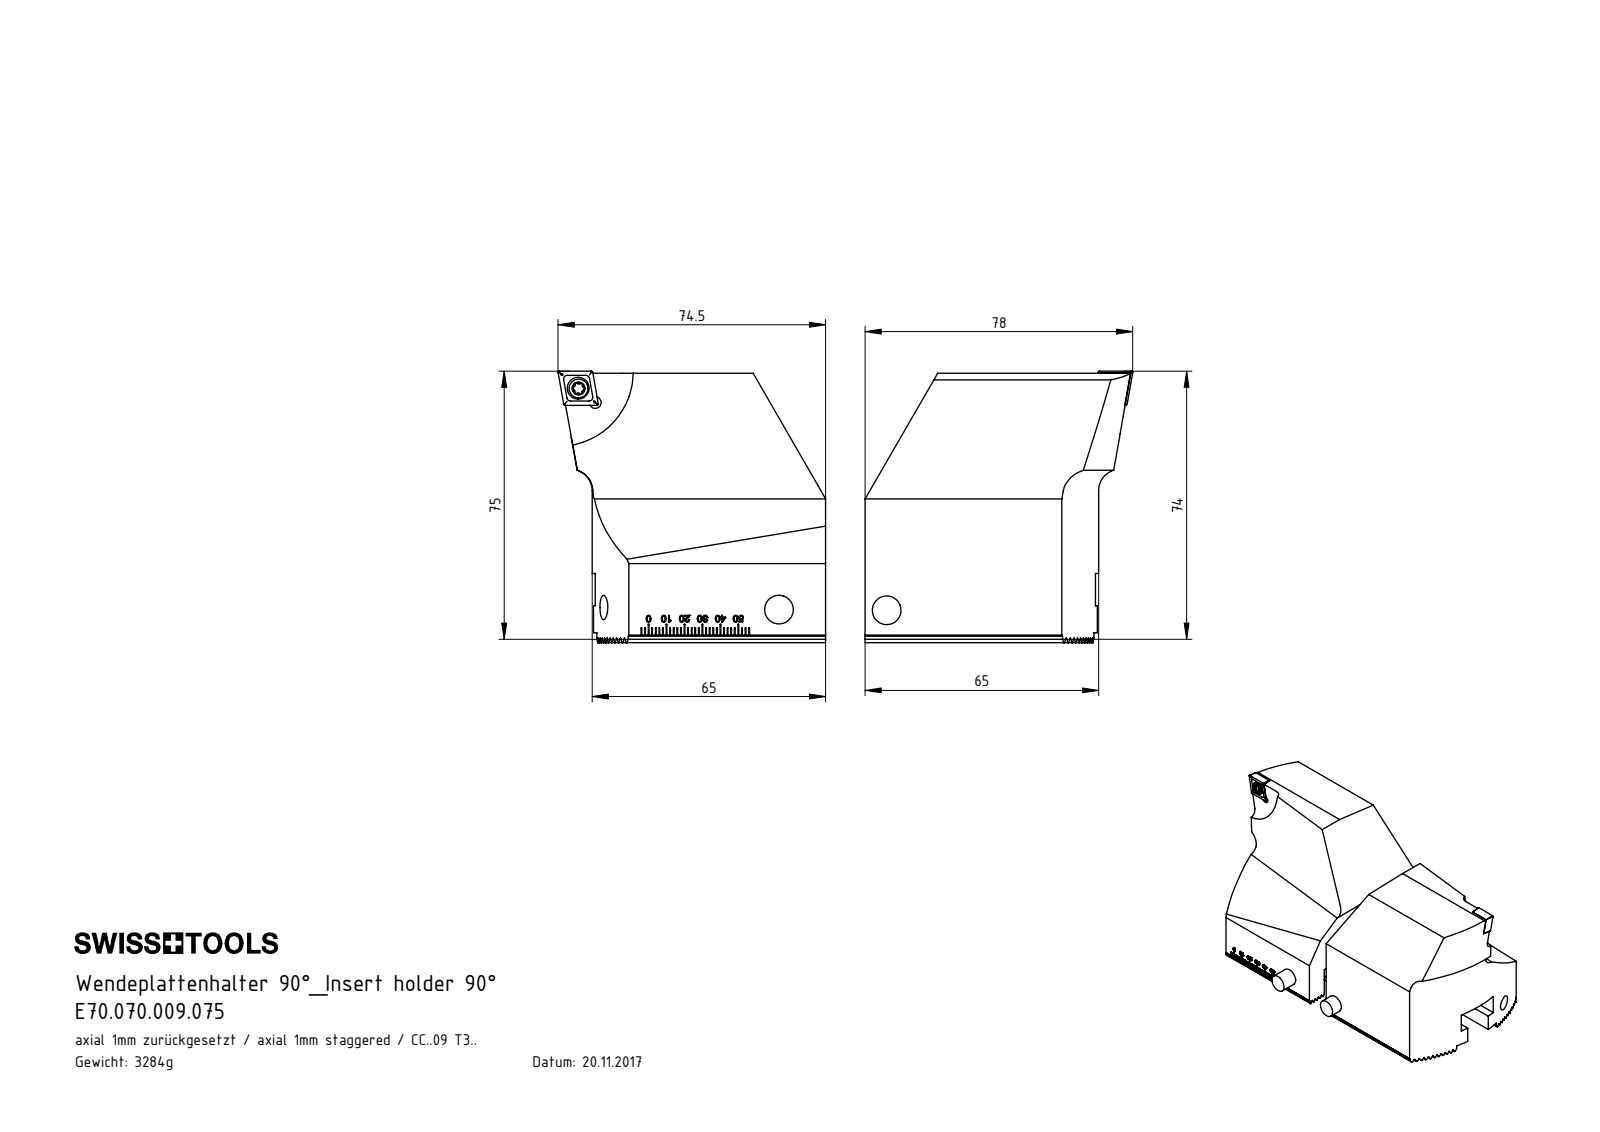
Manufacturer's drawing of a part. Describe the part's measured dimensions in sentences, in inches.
The part is named "VK1-WCB.001.075_A; WCB-ER2.001.009_A; CCMT09T304; E70.070.009.075 (+3 more)". Its 3-D file was written by "SolidWorks 2017 (CONFIG_CONTROL_DESIGN)". It is 12 solids with 1132 faces: 686 planar, 140 cylindrical and 306 other. Overall it measures 6.299 by 3.449 by 2.975 inches. Its volume is 25.65 cubic inches and its surface area 99.95 square inches. Round holes: 4 of diameter 0.13, 4 of diameter 0.315, 2 of diameter 0.173, 2 of diameter 0.24, 2 of diameter 0.268. Round bosses or shafts: 2 of diameter 0.315, 2 of diameter 0.217, 2 of diameter 0.207, 2 of diameter 0.157. Partial cylindrical surfaces (rounded edges, fillets, slot ends): 22 of radius 0.006, 12 of radius 0.013, 12 of radius 0.023, 2 of radius 0.157, 2 of radius 0.207, 2 of radius 0.827, 2 of radius 2.559, 2 of radius 2.717. The main face-to-face distances are 0.068, 0.341, 0.136, 2.756, 0.273, 0.205, 1.705, 0.965, 1.791, 0.409. The hole center spacings are 0.239, 0.244, 0.276, 1.181, 3.034, 3.229, 3.27, 3.275.
